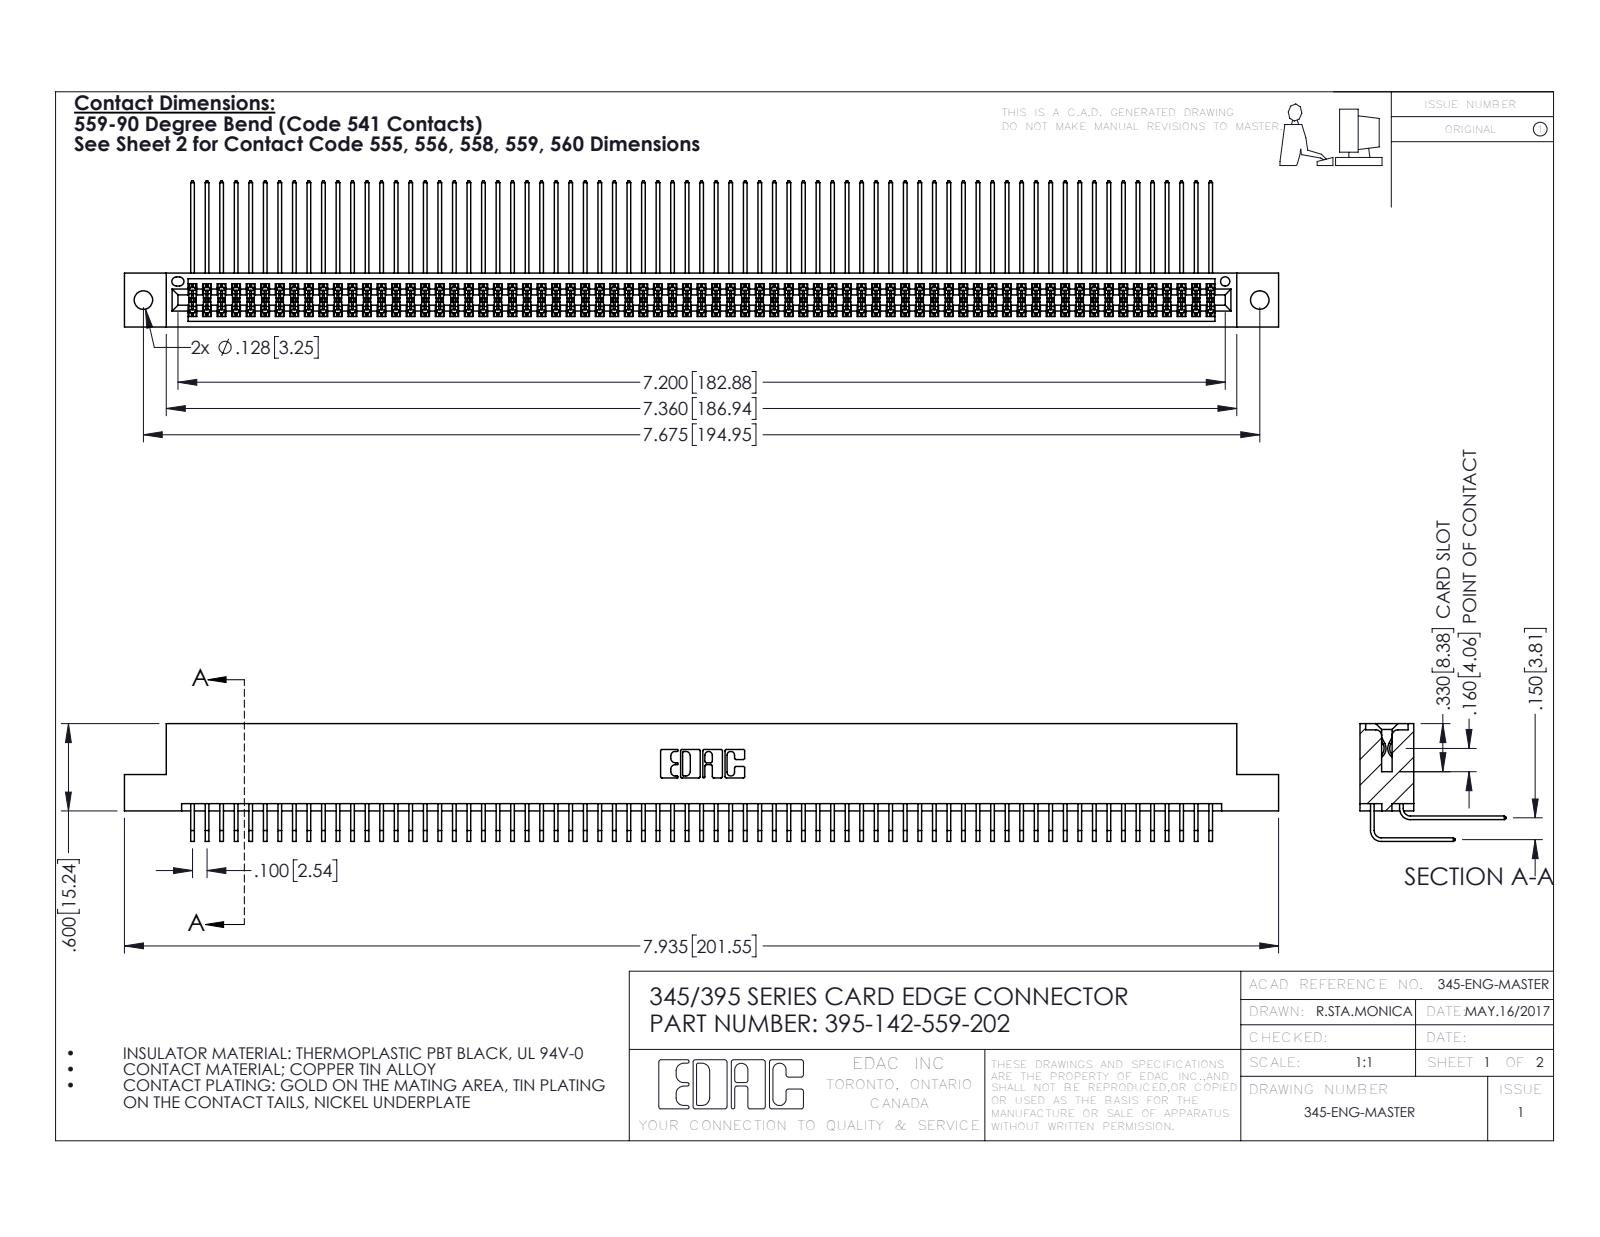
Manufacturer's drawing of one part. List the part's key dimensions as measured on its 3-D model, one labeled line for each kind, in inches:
Part name (STEP PRODUCT): 345-292-001_559 Tail - 2; 345 Part_Flush Mounting Lugs - 0.128 Dia; 345-292-001_558 559 Tail - 1; 395-142-559-202
STEP written by: SolidWorks 2016 (CONFIG_CONTROL_DESIGN)
Units: inches
Bodies: 143 solids, 7510 faces (5050 planar, 2460 cylindrical, 0 other)
Overall size (bounding box): 7.935 × 1.005 × 0.809
Volume: 1.259 in³ · Surface area: 53.69 in²
Round holes (diameter × count): ⌀0.128 ×2, ⌀0.064 ×1
Partial cylindrical surfaces — rounded edges, fillets, slot ends (radius × count): R0.006 ×283, R0.01 ×22, R0.007 ×6, R0.031 ×6, R0.026 ×3, R0.014 ×2, R0.019 ×2, R0.022 ×2
Main face-to-face distances: 0.072, 0.298, 0.2, 0.37, 0.098, 0.272, 0.025, 0.225, 0.175, 0.15
Hole centre spacings: 0.27, 7.439, 7.675
